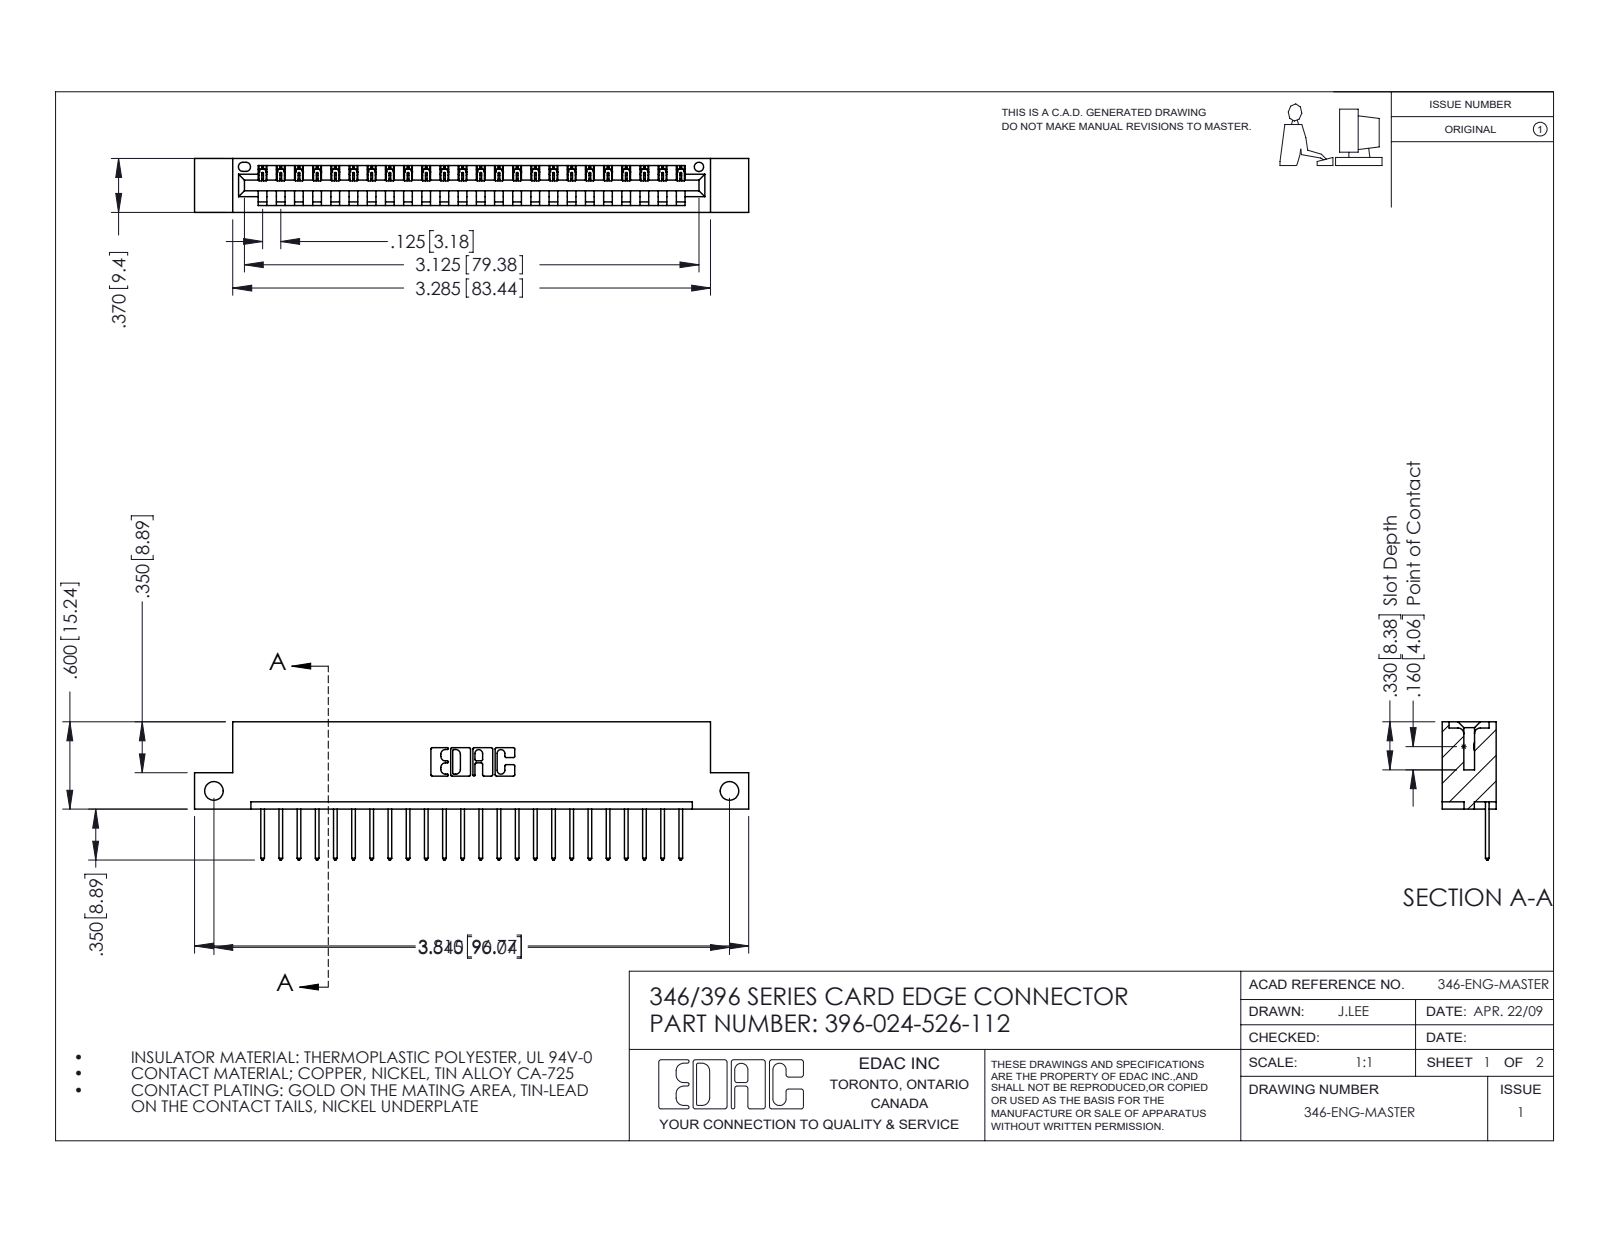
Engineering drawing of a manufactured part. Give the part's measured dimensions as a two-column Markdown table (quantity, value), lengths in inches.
| quantity | value |
| --- | --- |
| part name | 346 Part_Flush Mounting Lugs - Side Mount; 345-292-001_345-293-126; 396-024-526-112 |
| STEP written by | SolidWorks 2016 (CONFIG_CONTROL_DESIGN) |
| units | inches |
| bodies | 25 solids, 1514 faces (1036 planar, 478 cylindrical, 0 other) |
| overall size | 3.81 × 0.95 × 0.37 |
| volume | 0.551 in³ |
| surface area | 16.94 in² |
| round holes (diameter × count) | 0.128 × 2, 0.064 × 1 |
| partial cylindrical surfaces (radius × count) | 0.006 × 48, 0.01 × 48, 0.01 × 22, 0.007 × 6, 0.031 × 6, 0.026 × 3, 0.031 × 2, 0.04 × 2 |
| main face-to-face distances | 0.048, 0.322, 0.25, 0.37, 0.072, 0.298, 0.025, 0.148, 0.222, 0.1 |
| hole center spacings | 3.545 |
